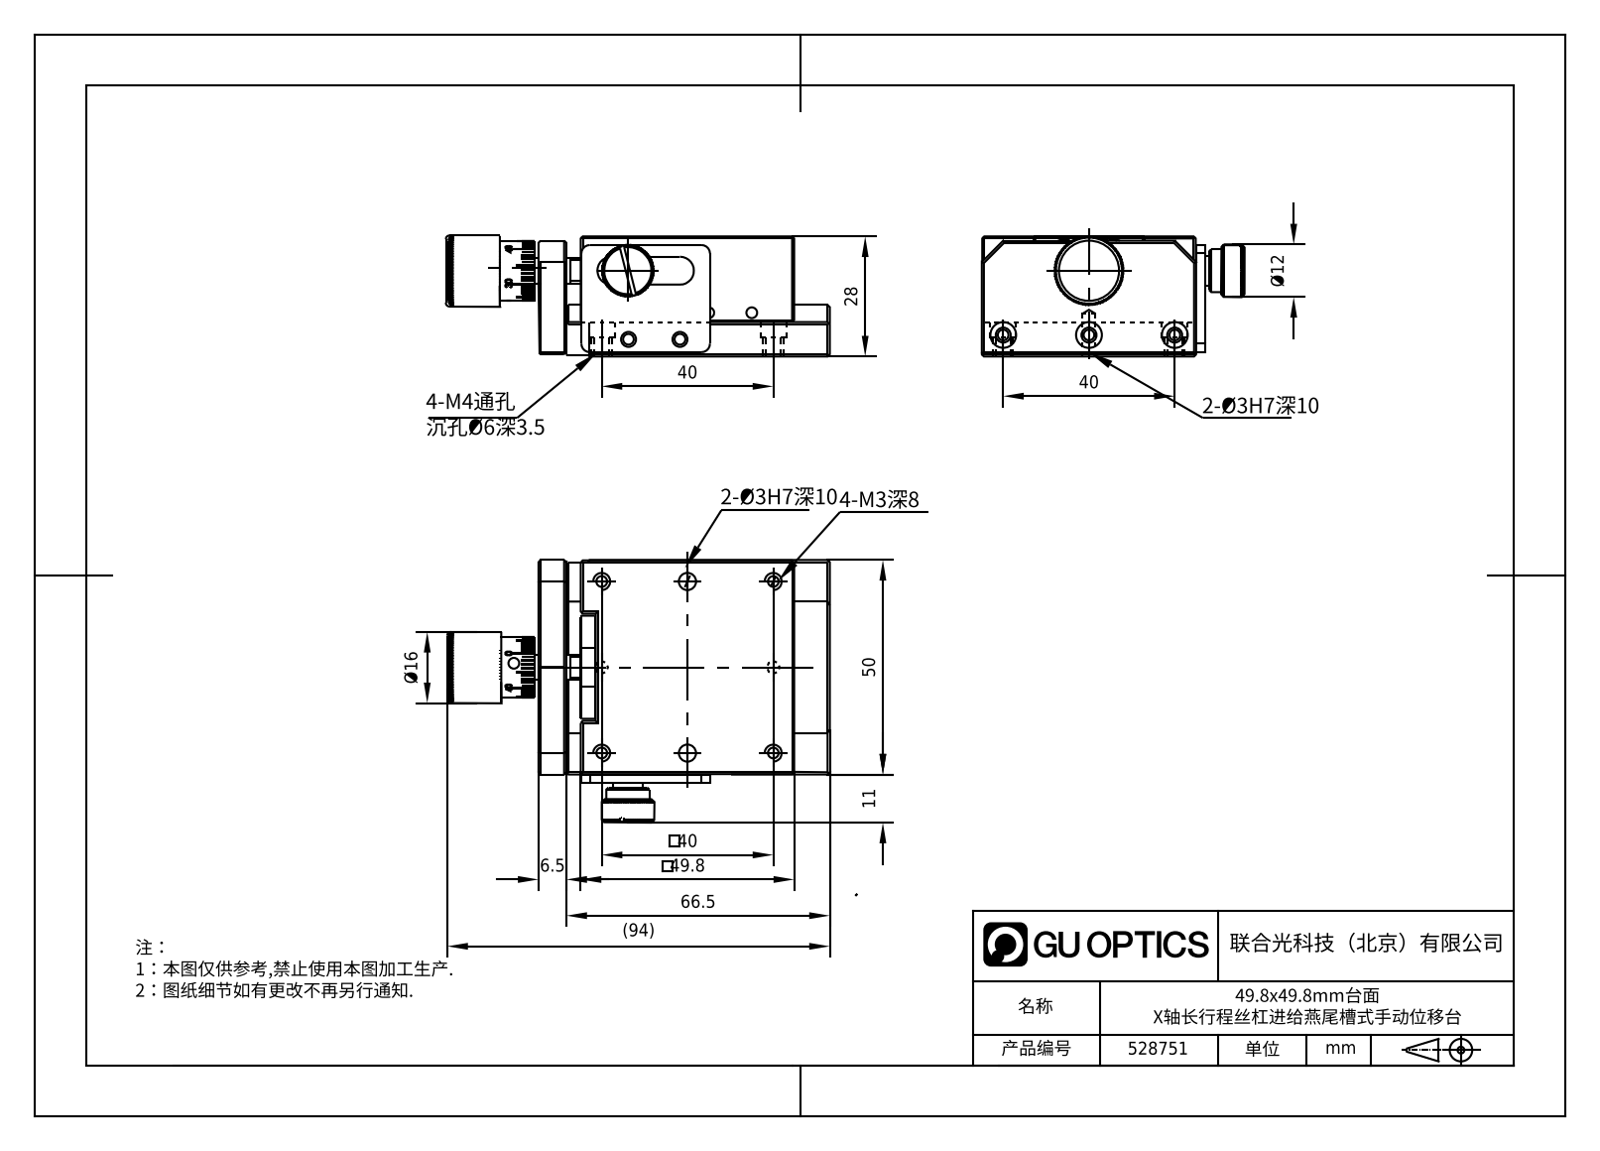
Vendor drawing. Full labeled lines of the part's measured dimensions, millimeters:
Part name (STEP PRODUCT): 528751
STEP written by: SolidWorks 2020 (CONFIG_CONTROL_DESIGN)
Units: millimetres
Bodies: 0 solids, 679 faces (338 planar, 165 cylindrical, 176 other)
Overall size (bounding box): 94 × 59.45 × 28
Round holes (diameter × count): ⌀2.5 ×12, ⌀2.05 ×6, ⌀3.4 ×6, ⌀3 ×5, ⌀2.9 ×4, ⌀5 ×4, ⌀6.5 ×4, ⌀6 ×3, ⌀1.5 ×2, ⌀3.1 ×2, ⌀3.3 ×1, ⌀3.5 ×1
Round bosses / shafts (diameter × count): ⌀3 ×5, ⌀4.5 ×4, ⌀2.5 ×4, ⌀5.6 ×2, ⌀5.5 ×2, ⌀13 ×1, ⌀12 ×1, ⌀10.3 ×1
Partial cylindrical surfaces — rounded edges, fillets, slot ends (radius × count): R0.3 ×8, R2 ×4, R2.1 ×2, R7.5 ×1, R11.5 ×1
Main face-to-face distances: 12, 4.5, 16, 20.5, 27.8, 11.8, 7.3, 7.5, 50, 4.7
Hole centre spacings: 20, 44.72, 8.5, 40, 28.28, 15, 13.6, 14.72
